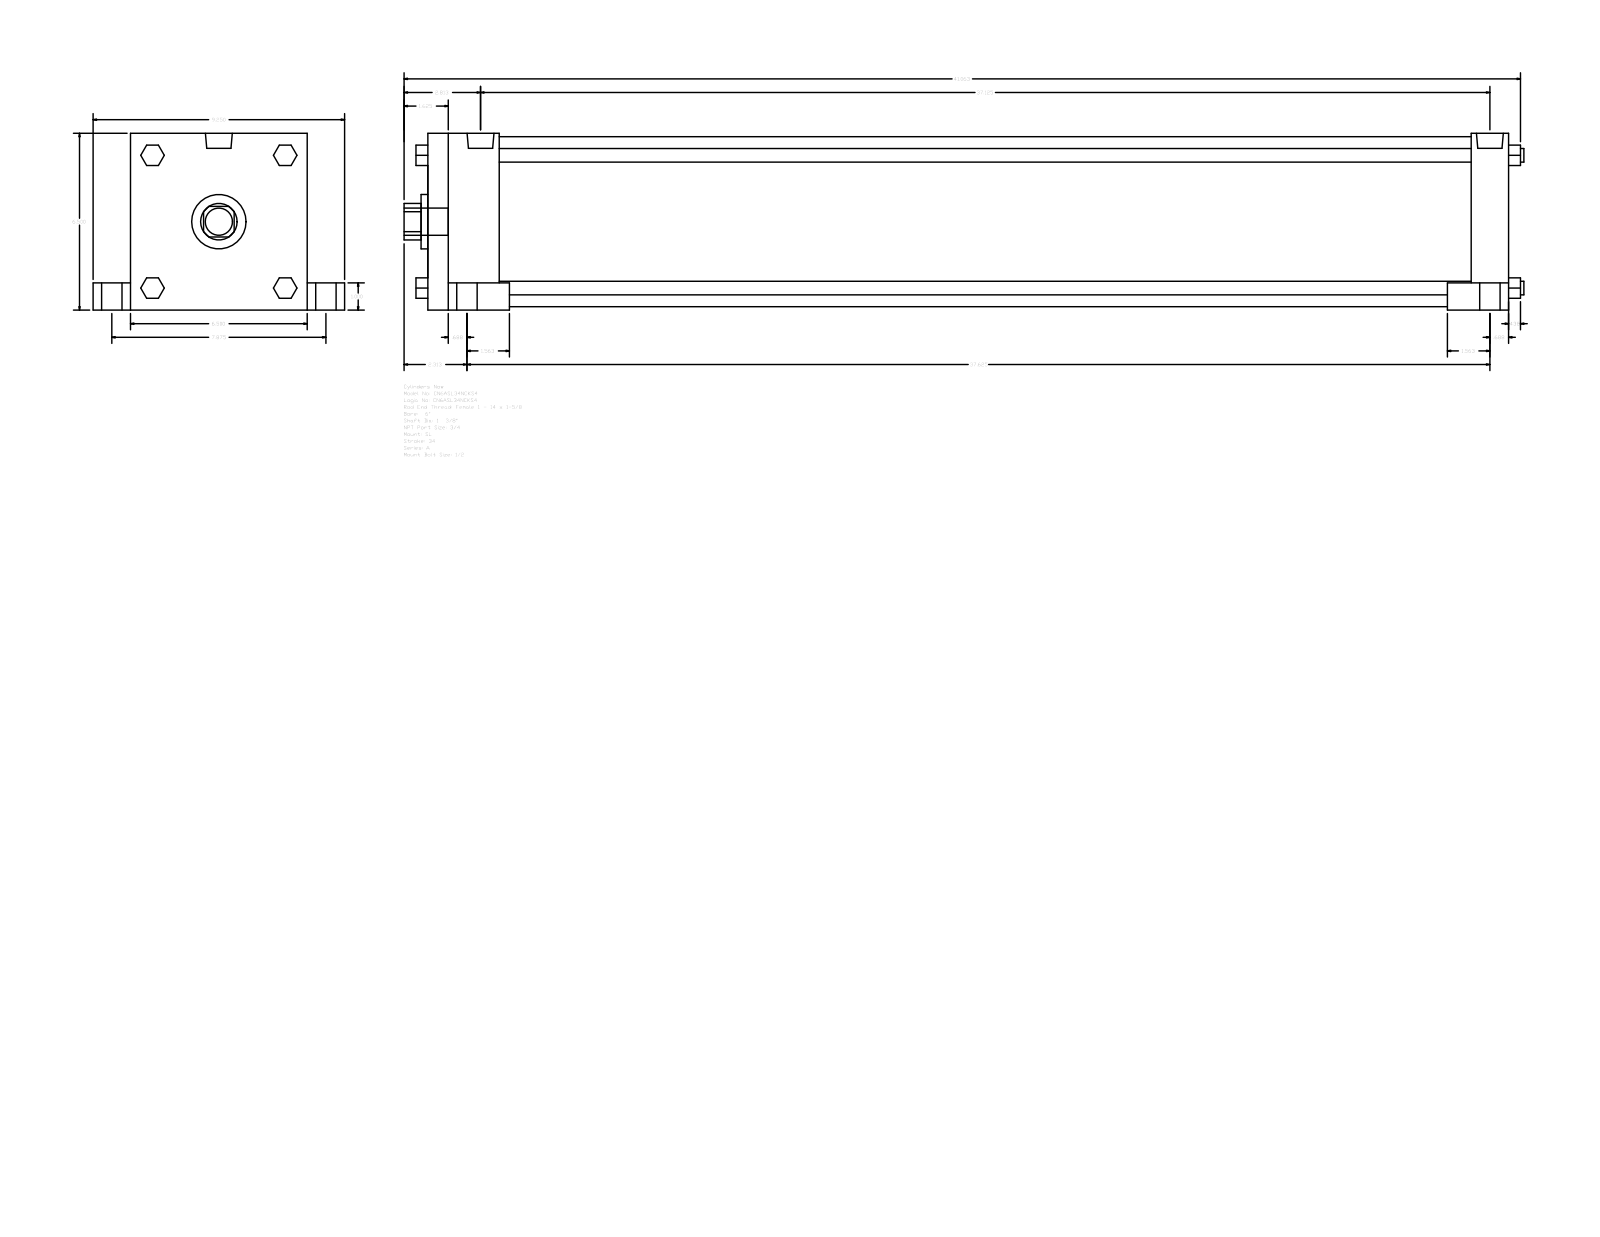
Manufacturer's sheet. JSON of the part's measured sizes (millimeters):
{"part_name": "A_SL__0600_1.375", "step_written_by": "GSSL Pune (CONFIG_CONTROL_DESIGN)", "units": "millimeters", "bodies": {"solids": 0, "faces": 150, "planar": 114, "cylindrical": 36, "other": 0}, "overall_size": [1046.16, 234.95, 165.1], "round_holes": [[34.92, 1], [50.8, 1], [158.75, 1]], "round_bosses_or_shafts": [[25.4, 5], [19.05, 4], [15.08, 4], [12.7, 4], [25.12, 2]], "partial_cylinders_radius": [[17.06, 1]], "face_to_face_distances": [165.1, 1009.65, 66.67, 942.98, 974.72, 908.05, 34.93, 25.4, 139.7, 34.92]}
